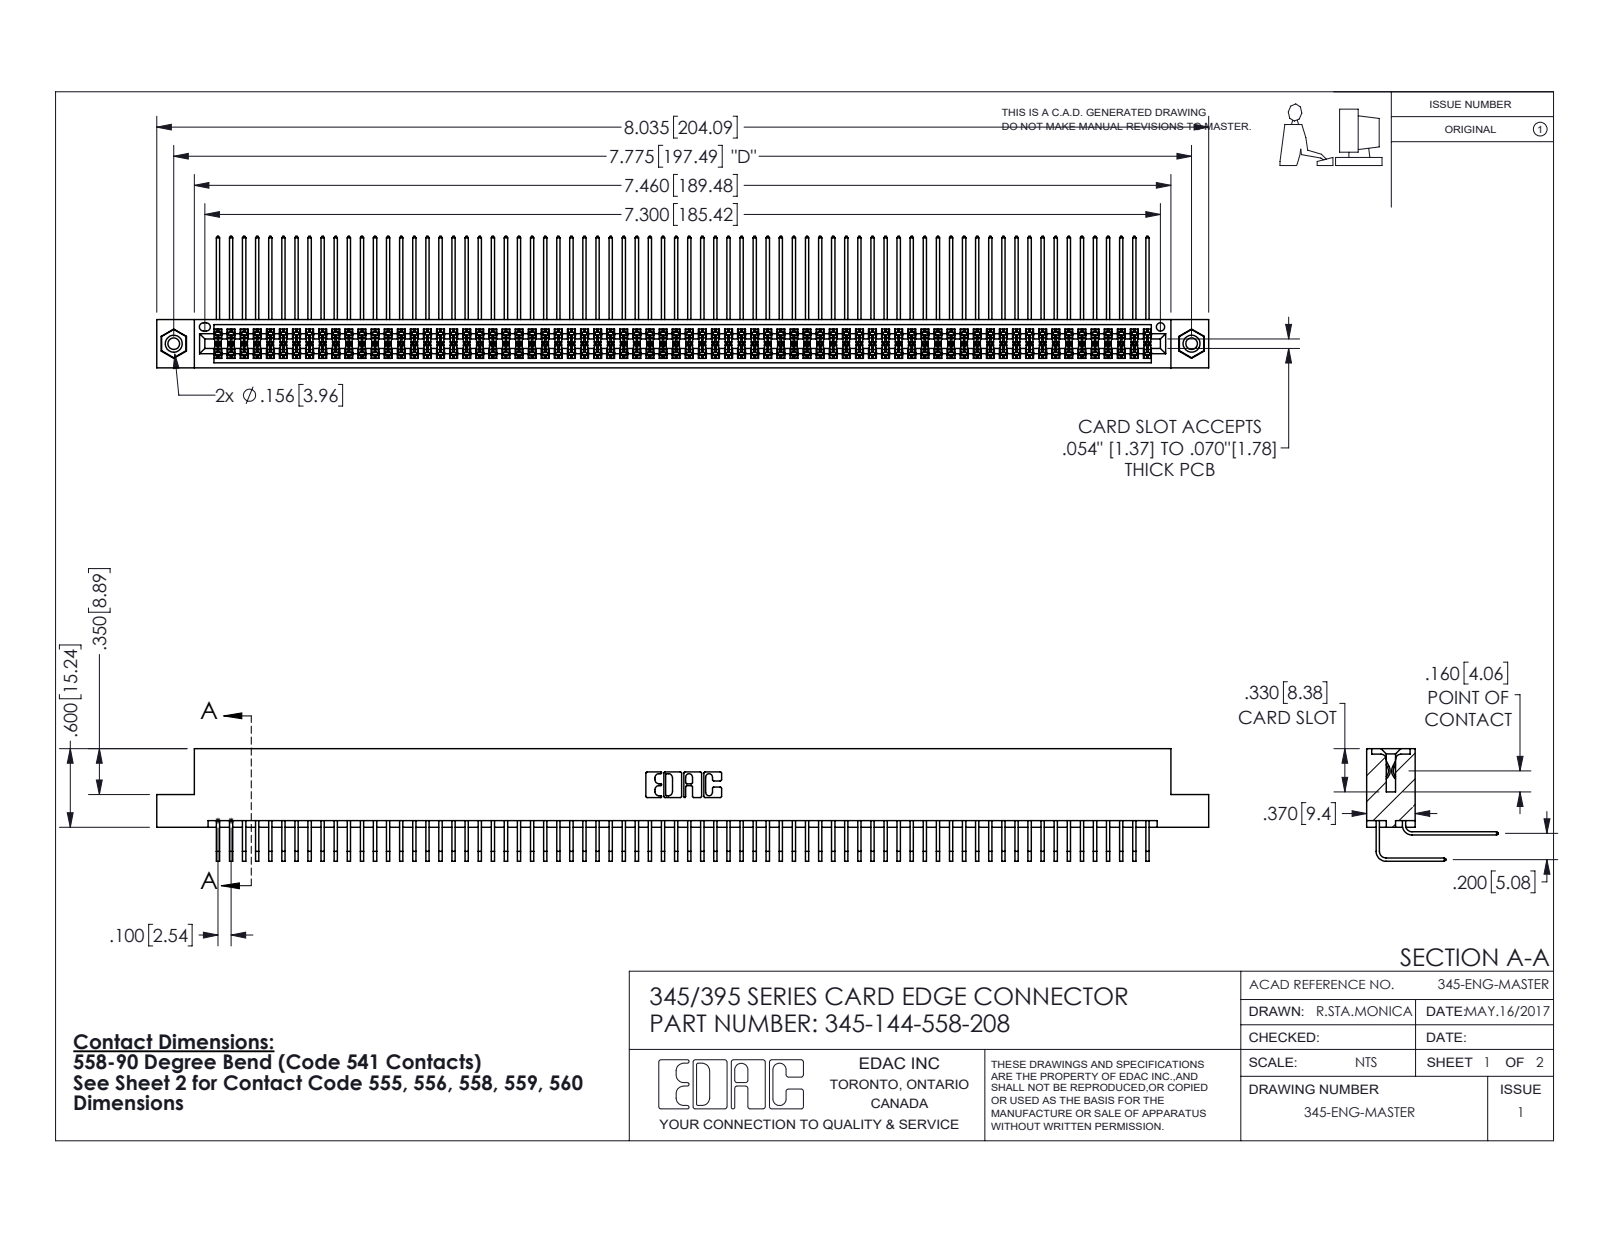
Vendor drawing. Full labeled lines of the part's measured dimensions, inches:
Part name (STEP PRODUCT): 345-250-001_345-250-003-102; 345 Part_Flush Mounting Lugs - 0.156 Dia-TI; 345-292-001_558 559 Tail - 1; 345-292-001_558 Tail - 2 (+1 more)
STEP written by: SolidWorks 2016 (CONFIG_CONTROL_DESIGN)
Units: inches
Bodies: 147 solids, 7674 faces (5152 planar, 2506 cylindrical, 16 other)
Overall size (bounding box): 8.035 × 1.005 × 0.859
Volume: 1.277 in³ · Surface area: 54.93 in²
Round holes (diameter × count): ⌀0.089 ×2, ⌀0.125 ×2, ⌀0.156 ×2, ⌀0.064 ×1
Round bosses / shafts (diameter × count): ⌀0.155 ×2
Partial cylindrical surfaces — rounded edges, fillets, slot ends (radius × count): R0.006 ×288, R0.01 ×22, R0.007 ×6, R0.031 ×6, R0.026 ×3, R0.014 ×2, R0.019 ×2, R0.022 ×2
Main face-to-face distances: 0.072, 0.298, 0.2, 0.37, 0.098, 0.272, 0.025, 0.225, 0.025, 0.175
Hole centre spacings: 0.27, 7.539, 7.775
